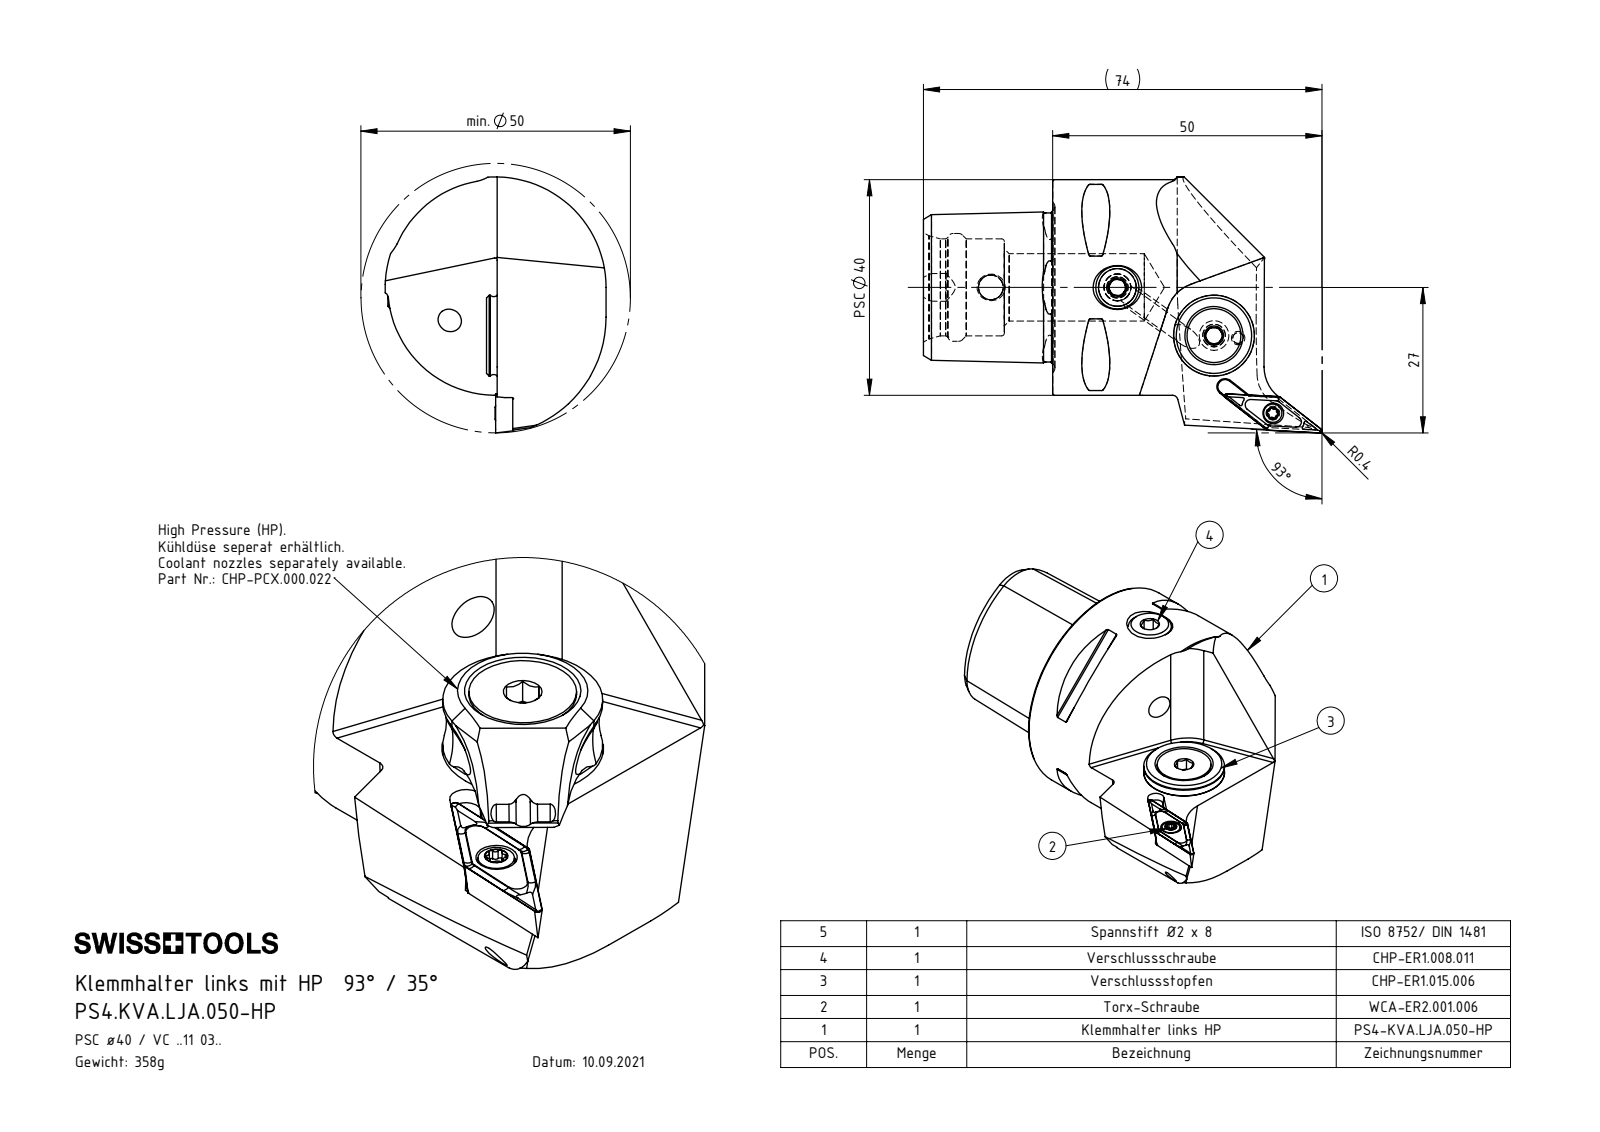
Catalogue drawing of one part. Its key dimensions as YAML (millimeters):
part_name: "PS4.KVA.LJA.050-HP; DIN 3771 - 13x1; CHP-PCX.000.022_Düse; ISO 8752 2x8 (+7 more)"
step_written_by: "SolidWorks 2022 (CONFIG_CONTROL_DESIGN)"
units: millimeters
bodies: {solids: 9, faces: 487, planar: 106, cylindrical: 133, other: 248}
overall_size: [73.98, 47.49, 41]
volume: 46355
surface_area: 15438
round_holes:
  - {diameter: 4.2, count: 2}
  - {diameter: 1.2, count: 1}
  - {diameter: 2, count: 1}
  - {diameter: 2.05, count: 1}
  - {diameter: 2.8, count: 1}
  - {diameter: 3, count: 1}
  - {diameter: 3.3, count: 1}
  - {diameter: 3.85, count: 1}
  - {diameter: 4, count: 1}
  - {diameter: 4.6, count: 1}
  - {diameter: 5, count: 1}
  - {diameter: 5.3, count: 1}
round_bosses_or_shafts:
  - {diameter: 40, count: 1}
  - {diameter: 14.85, count: 1}
  - {diameter: 13.4, count: 1}
  - {diameter: 10, count: 1}
  - {diameter: 8, count: 1}
  - {diameter: 5.5, count: 1}
  - {diameter: 5, count: 1}
  - {diameter: 3.4, count: 1}
partial_cylinders:
  - {radius: 0.3, count: 9}
  - {radius: 1, count: 7}
  - {radius: 0.21, count: 6}
  - {radius: 0.36, count: 4}
  - {radius: 0.5, count: 4}
  - {radius: 6, count: 3}
  - {radius: 0.36, count: 2}
  - {radius: 1.1, count: 2}
face_to_face_distances: [24, 4.5, 15.52, 1.5, 3, 1.62, 2.88, 15.7, 35.3, 17.2]
hole_center_spacings: [4.49, 15.35, 15.41, 18.07, 18.14, 20.04, 23.5, 24.3]
